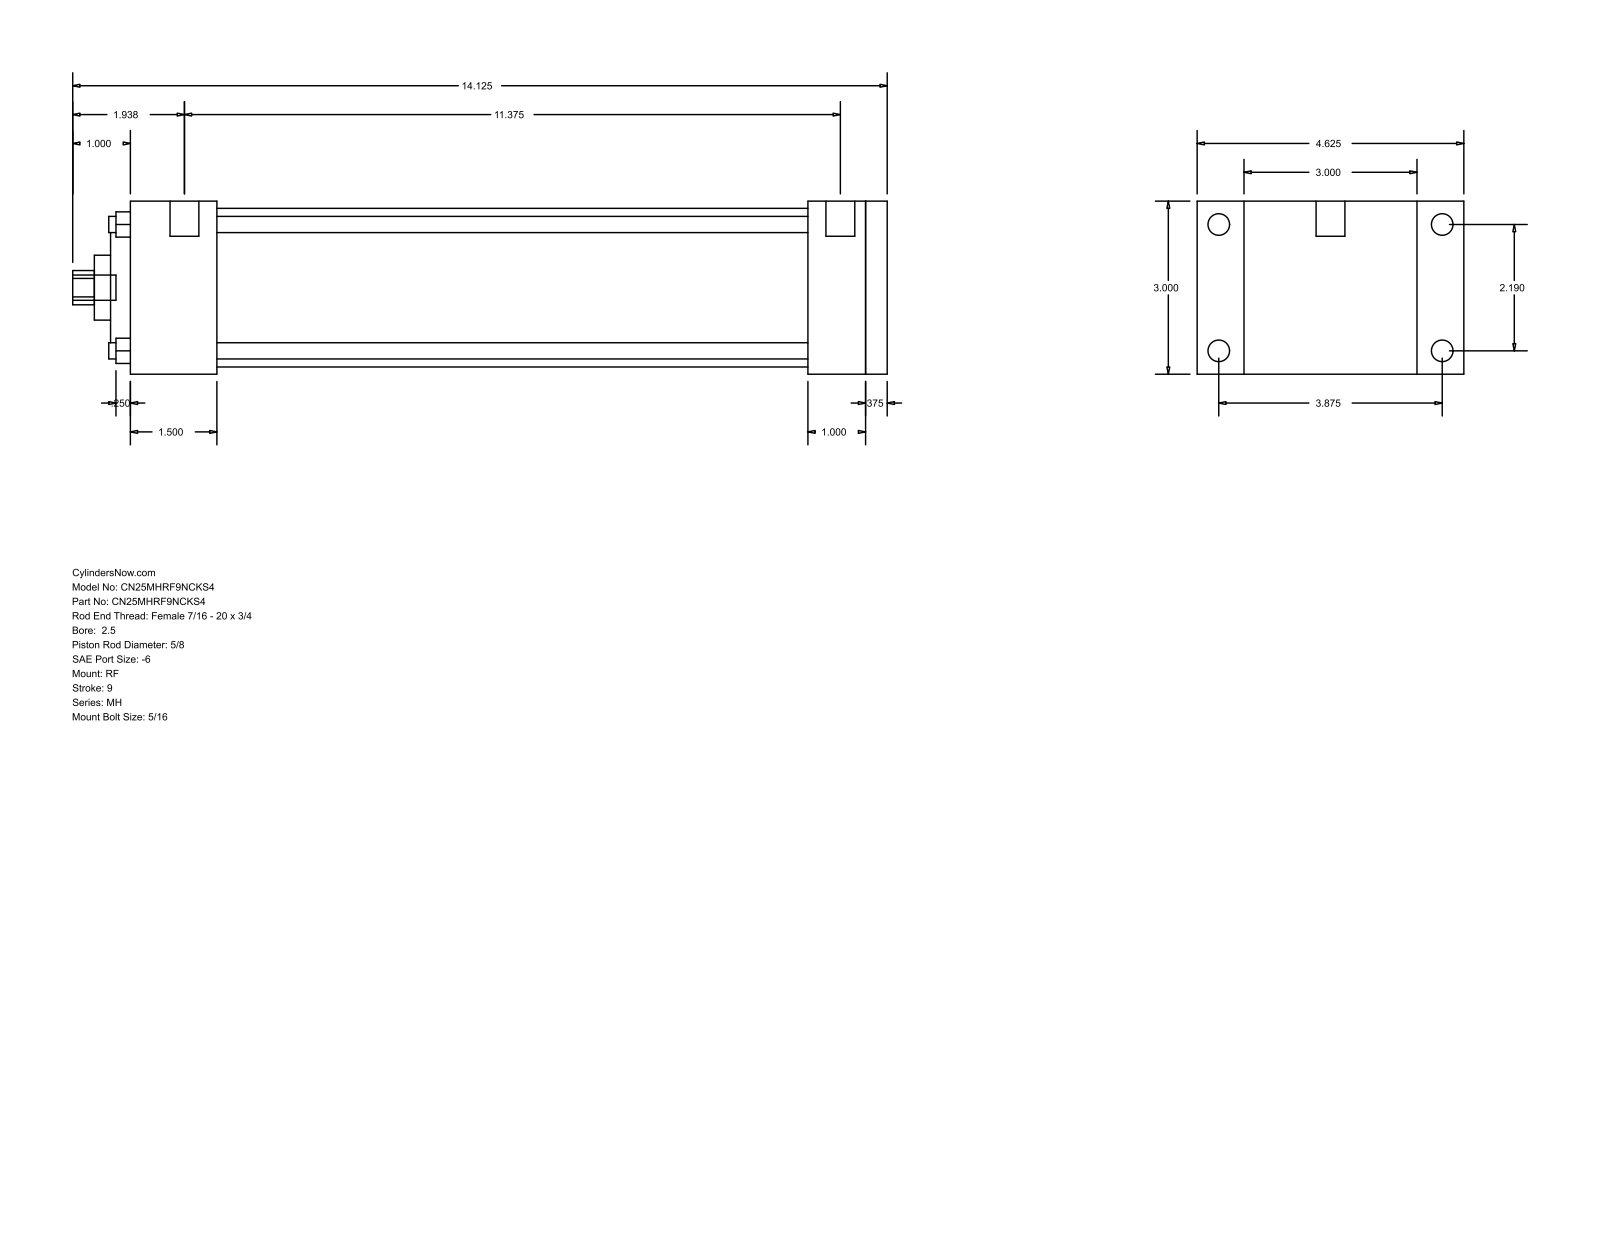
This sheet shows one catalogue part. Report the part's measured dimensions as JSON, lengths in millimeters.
{"part_name": "MH_RF__0250_0.625", "step_written_by": "GSSL Pune (CONFIG_CONTROL_DESIGN)", "units": "millimeters", "bodies": {"solids": 0, "faces": 94, "planar": 65, "cylindrical": 29, "other": 0}, "overall_size": [358.77, 117.47, 76.2], "round_holes": [[7.14, 4], [15.88, 1], [28.57, 1], [55.55, 1], [69.85, 1]], "round_bosses_or_shafts": [[9.53, 4], [5.56, 4], [12.7, 2], [11.11, 1]], "partial_cylinders_radius": [[7.54, 1]], "face_to_face_distances": [76.2, 9.52, 333.37, 323.85, 25.4, 298.45, 34.92, 38.1, 260.35, 285.75], "hole_center_spacings": [39.33, 55.62, 78.66]}
